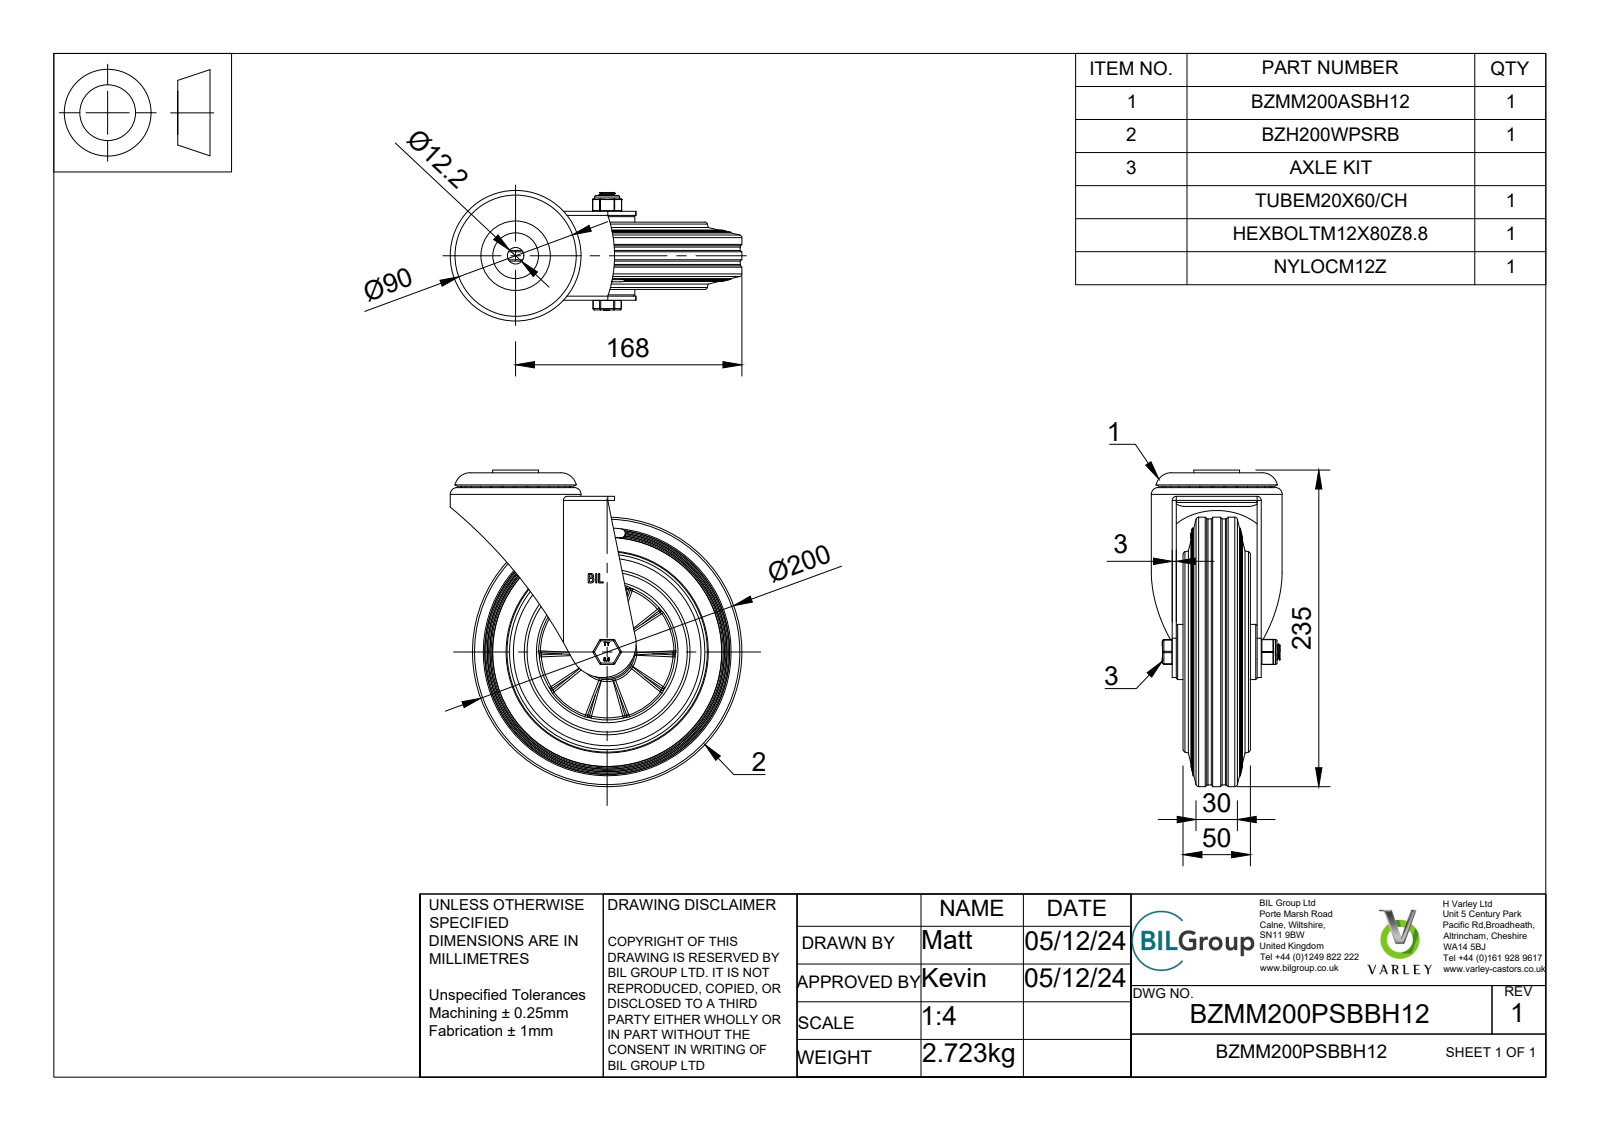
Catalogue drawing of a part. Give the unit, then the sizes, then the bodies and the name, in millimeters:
Units: millimetres
Overall size (bounding box): 235 × 216.5 × 97
Round holes (diameter × count): ⌀12 ×1, ⌀12.2 ×1, ⌀12.3 ×1, ⌀12.5 ×1, ⌀14 ×1, ⌀20 ×1, ⌀35 ×1, ⌀51 ×1, ⌀58 ×1, ⌀91 ×1, ⌀101 ×1, ⌀118 ×1
Round bosses / shafts (diameter × count): ⌀7.5 ×8, ⌀34 ×2, ⌀200 ×1, ⌀197.5 ×1, ⌀123 ×1, ⌀97 ×1, ⌀63 ×1, ⌀41 ×1
Partial cylindrical surfaces — rounded edges, fillets, slot ends (radius × count): R0.5 ×18, R1 ×12, R1.5 ×4, R3 ×2, R13.5 ×1, R25 ×1, R92.5 ×1, R358.69 ×1
Main face-to-face distances: 3, 63, 14, 49, 6.5, 2.5, 9.5, 11, 60, 7.5
Volume: 1 217 000 mm³ · Surface area: 299 019 mm²
Bodies: 63 solids, 817 faces (206 planar, 151 cylindrical, 460 other)
Part name (STEP PRODUCT): BZMM200PSBBH12 v3; BZMM200ASBH12 v1; ZINC PLATED, PRESSED STEEL HEAD; ZINC PLATED, PRESSED STEEL HEAD Geometry (+6 more)
STEP written by: Autodesk Translation Framework v13.20.0.188 (AP242_MANAGED_MODEL_BASED_3D_ENGINEERING_MIM_LF)
